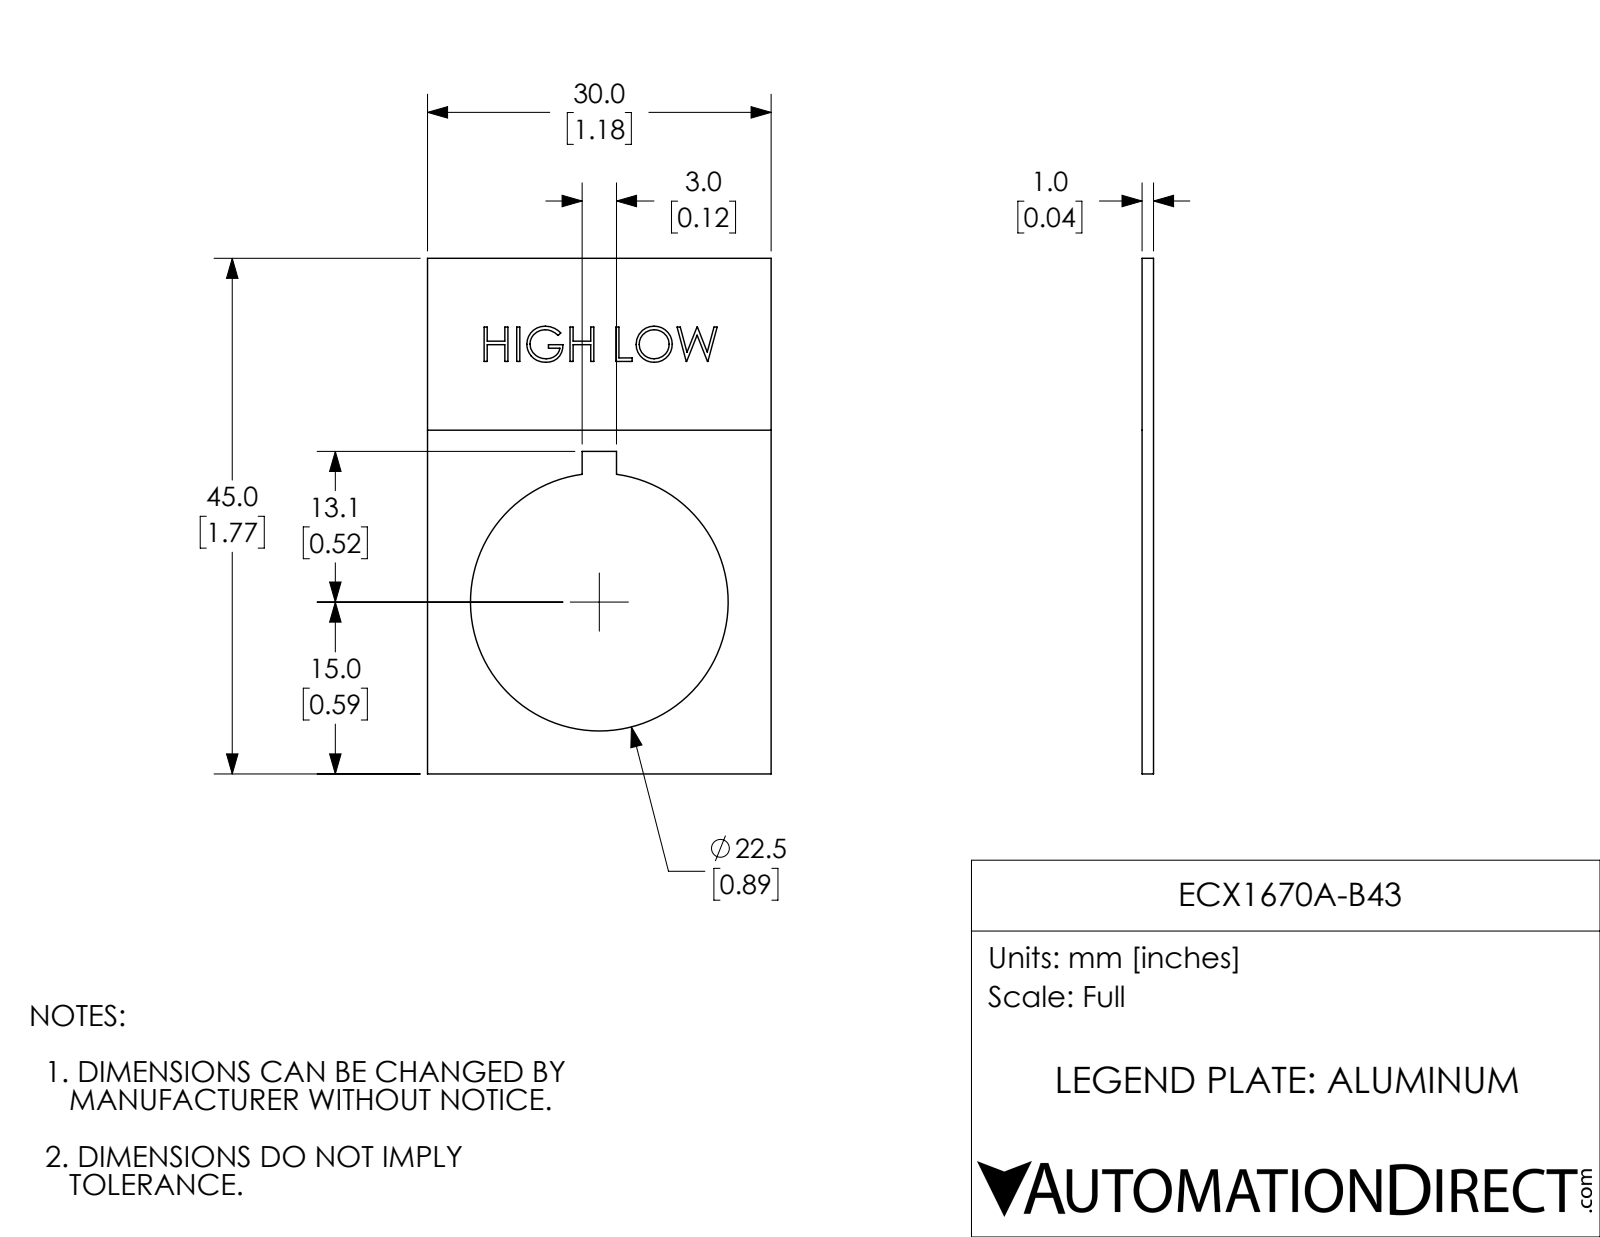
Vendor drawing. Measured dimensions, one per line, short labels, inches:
name: ECX1670A-B43
written by: SolidWorks 2017 (AUTOMOTIVE_DESIGN)
unit: in
bodies: 1 solid, 89 faces (69 planar, 3 cylindrical, 17 other)
size: 1.772 × 1.181 × 0.039
volume: 0.058 in³; area: 3.287 in²
holes: 1× ⌀0.886
face distances: 0.039, 1.181, 1.772, 0.038, 0.531, 0.65, 1.108, 0.663, 0.118, 0.295
